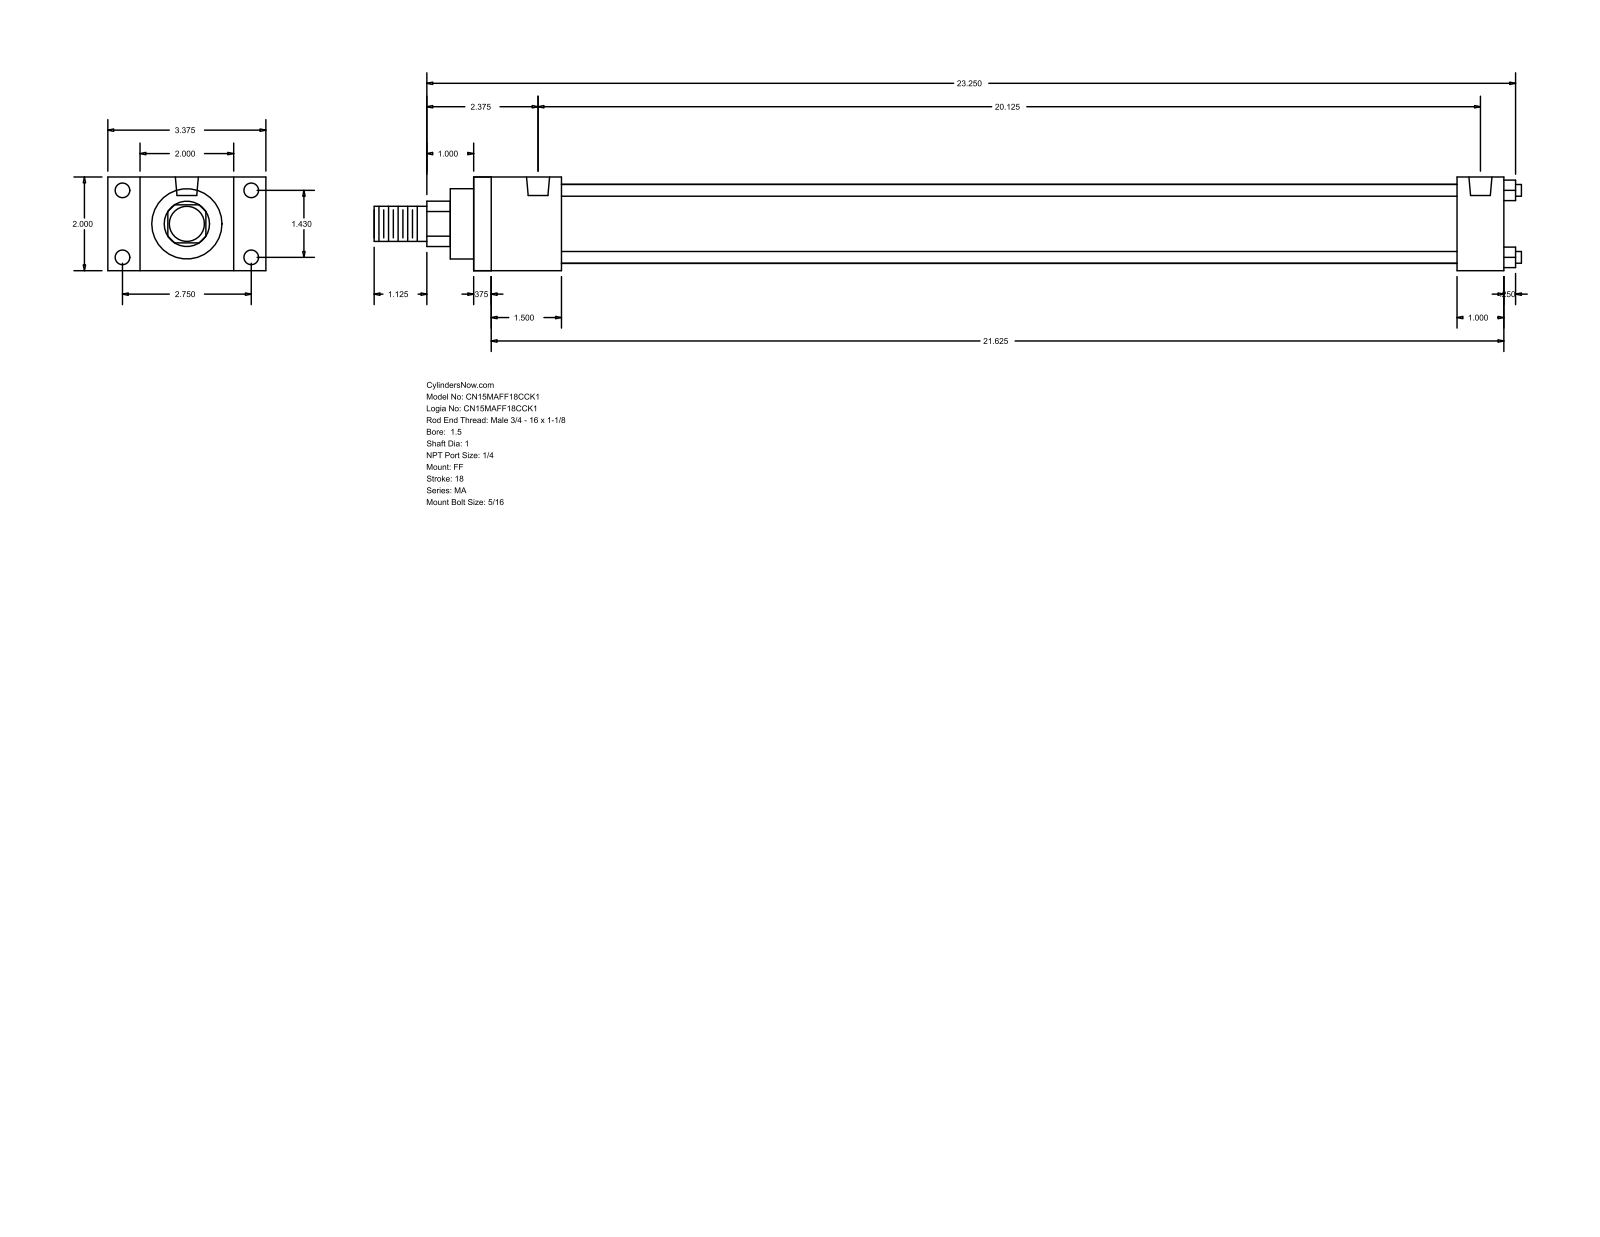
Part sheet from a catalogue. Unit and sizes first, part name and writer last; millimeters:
Units: millimetres
Overall size (bounding box): 622.3 × 85.72 × 50.8
Round holes (diameter × count): ⌀7.94 ×8, ⌀12.49 ×2
Round bosses / shafts (diameter × count): ⌀6.35 ×4, ⌀42.93 ×1, ⌀38.1 ×1, ⌀25.4 ×1, ⌀19.05 ×1
Partial cylindrical surfaces — rounded edges, fillets, slot ends (radius × count): R12.29 ×1
Main face-to-face distances: 50.8, 558.8, 9.52, 549.28, 25.4, 47.63, 533.4, 38.11, 523.88, 485.77
Hole centre spacings: 36.32, 69.84, 78.72, 511.17
Bodies: 0 solids, 92 faces (64 planar, 28 cylindrical, 0 other)
Part name (STEP PRODUCT): MA_FF__0150_1
STEP written by: GSSL Pune (CONFIG_CONTROL_DESIGN)
